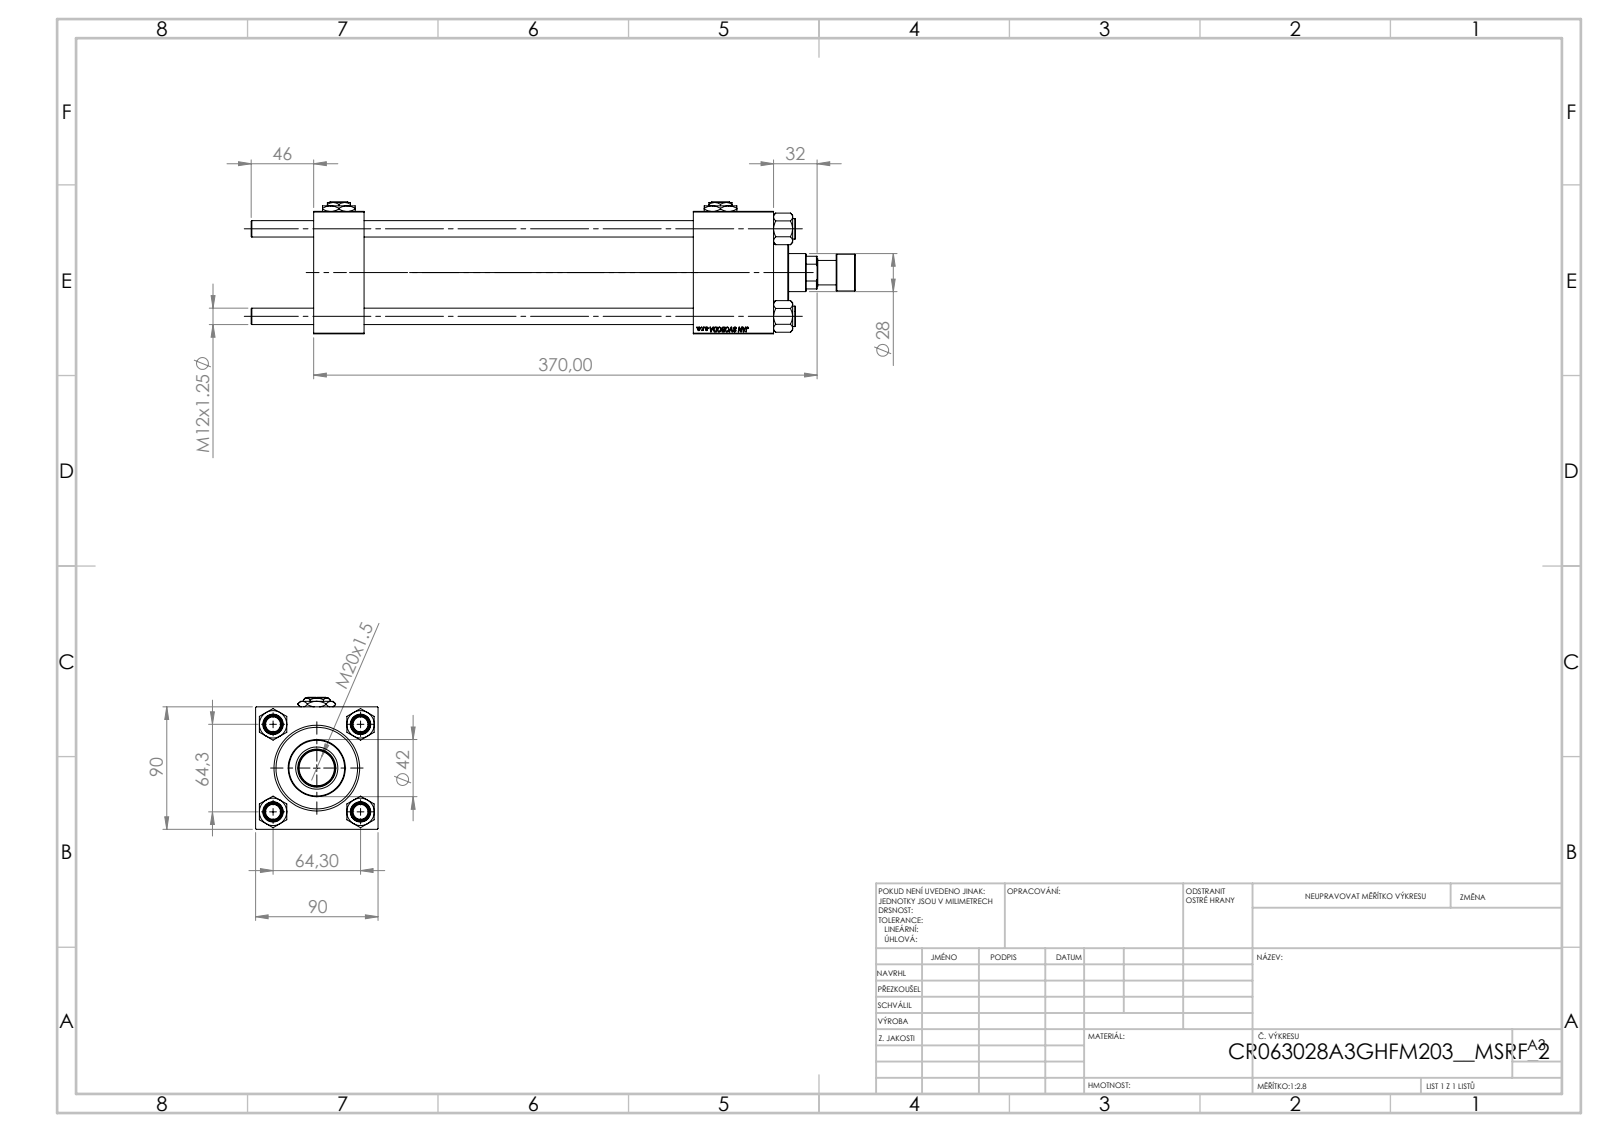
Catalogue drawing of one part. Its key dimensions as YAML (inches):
part_name: "Zatka_pro_OIL_PORT; CR025_012_A_0_G_A_G_M_020_+#_##_TYCINKA; V215CR_ROD_END_F; V215_VC_A (+3 more)"
step_written_by: "SolidWorks 2019 (CONFIG_CONTROL_DESIGN)"
units: inches
bodies: {solids: 14, faces: 1247, planar: 571, cylindrical: 92, other: 584}
overall_size: [17.48, 3.819, 3.543]
volume: 79.09
surface_area: 500.5
round_holes:
  - {diameter: 0.472, count: 4}
  - {diameter: 0.276, count: 2}
  - {diameter: 0.825, count: 2}
  - {diameter: 1.181, count: 2}
  - {diameter: 0.728, count: 1}
  - {diameter: 1.102, count: 1}
  - {diameter: 1.22, count: 1}
  - {diameter: 1.969, count: 1}
  - {diameter: 2.362, count: 1}
  - {diameter: 2.48, count: 1}
round_bosses_or_shafts:
  - {diameter: 0.591, count: 4}
  - {diameter: 2.717, count: 1}
  - {diameter: 1.654, count: 1}
  - {diameter: 1.063, count: 1}
  - {diameter: 0.709, count: 1}
face_to_face_distances: [3.543, 1.457, 13.307, 11.85, 2.323, 10.984, 9.528, 12.177, 10.72, 1.193]
hole_center_spacings: [1.79, 2.531, 3.58, 11.043]
